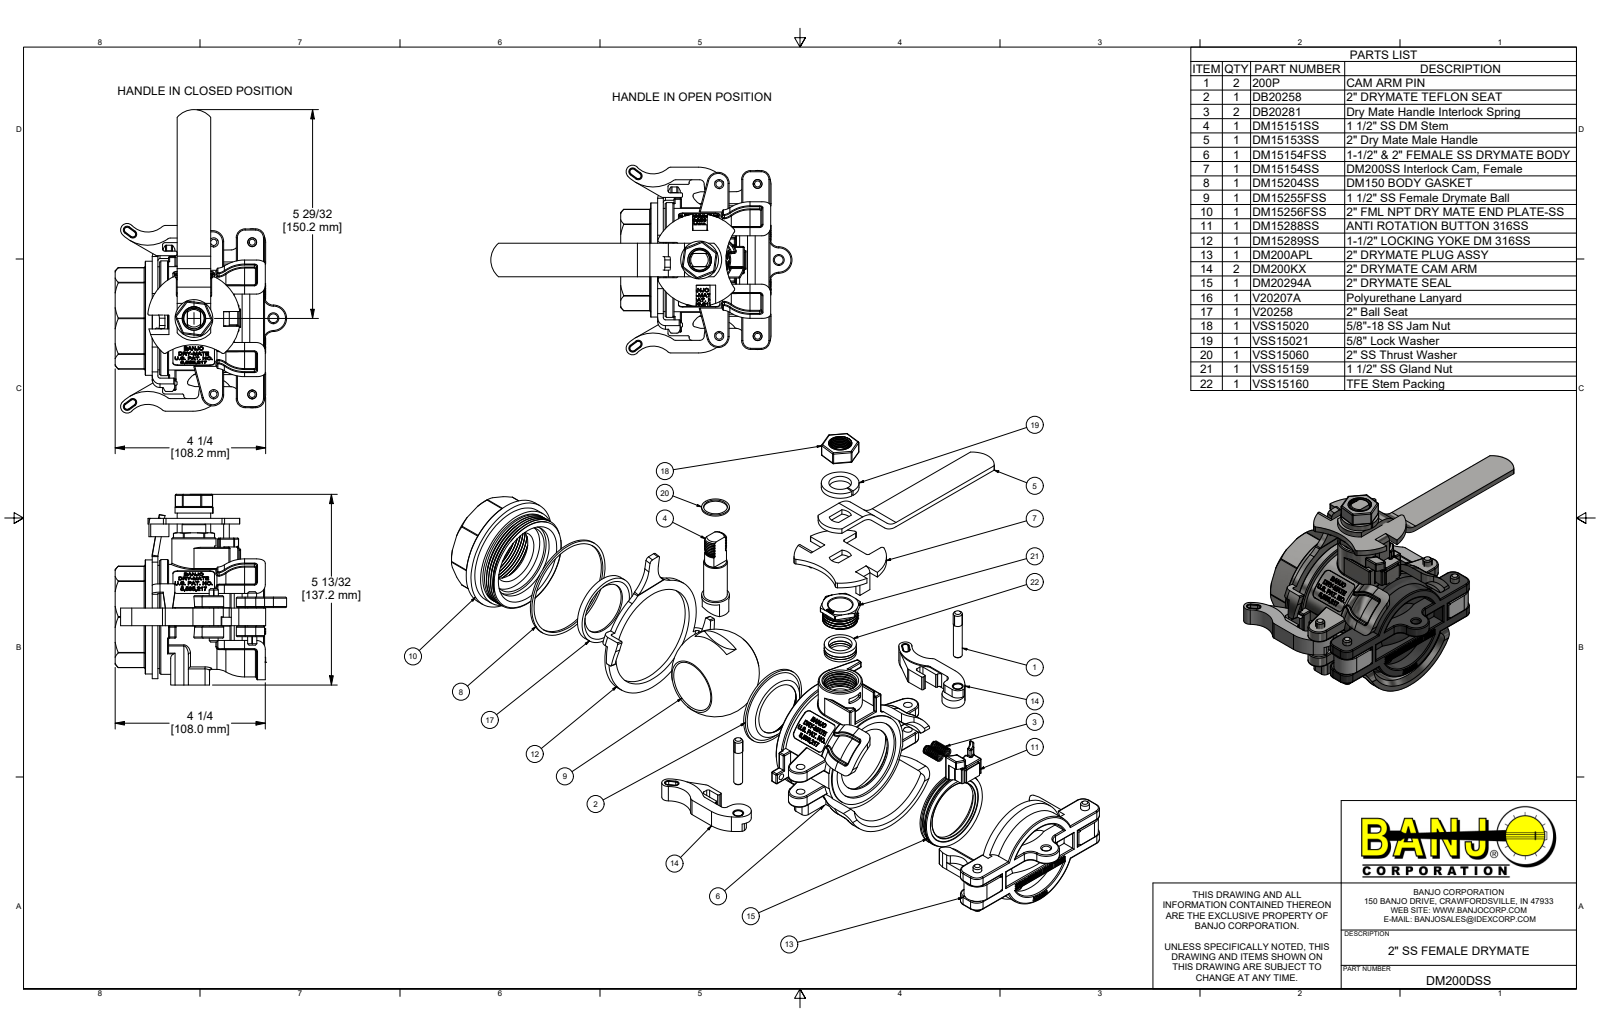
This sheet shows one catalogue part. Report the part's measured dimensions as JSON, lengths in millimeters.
{"part_name": "DM200DSS; DM15154FSS; DB20258; DB20281 (+8 more)", "step_written_by": "Autodesk Inventor 2019 (AUTOMOTIVE_DESIGN)", "units": "millimeters", "bodies": {"solids": 35, "faces": 3041, "planar": 1200, "cylindrical": 725, "other": 1116}, "overall_size": [346.3, 150.2, 137.3], "volume_mm3": 471100, "surface_area_mm2": 218800, "round_holes": [[6.4, 5], [6.5, 4], [3.2, 3], [38.1, 2], [4.6, 1], [14.7, 1], [16.3, 1], [16.8, 1], [17, 1], [17.2, 1], [17.5, 1], [21.3, 1]], "round_bosses_or_shafts": [[6.6, 4], [6.3, 4], [7.1, 3], [88.9, 1], [82, 1], [81, 1], [75.6, 1], [75.4, 1]], "partial_cylinders_radius": [[0.8, 177], [1.5, 25], [3, 10], [3.2, 10], [6.4, 10], [2, 9], [0.8, 6], [25.4, 6]], "face_to_face_distances": [7.6, 4.1, 3.8, 42.7, 55.4, 21.8, 21.8, 7.9, 20.6, 34.8], "hole_center_spacings": [24.1, 27.7, 41.8, 56.4, 56.8, 57.1, 68.9, 69.5]}
